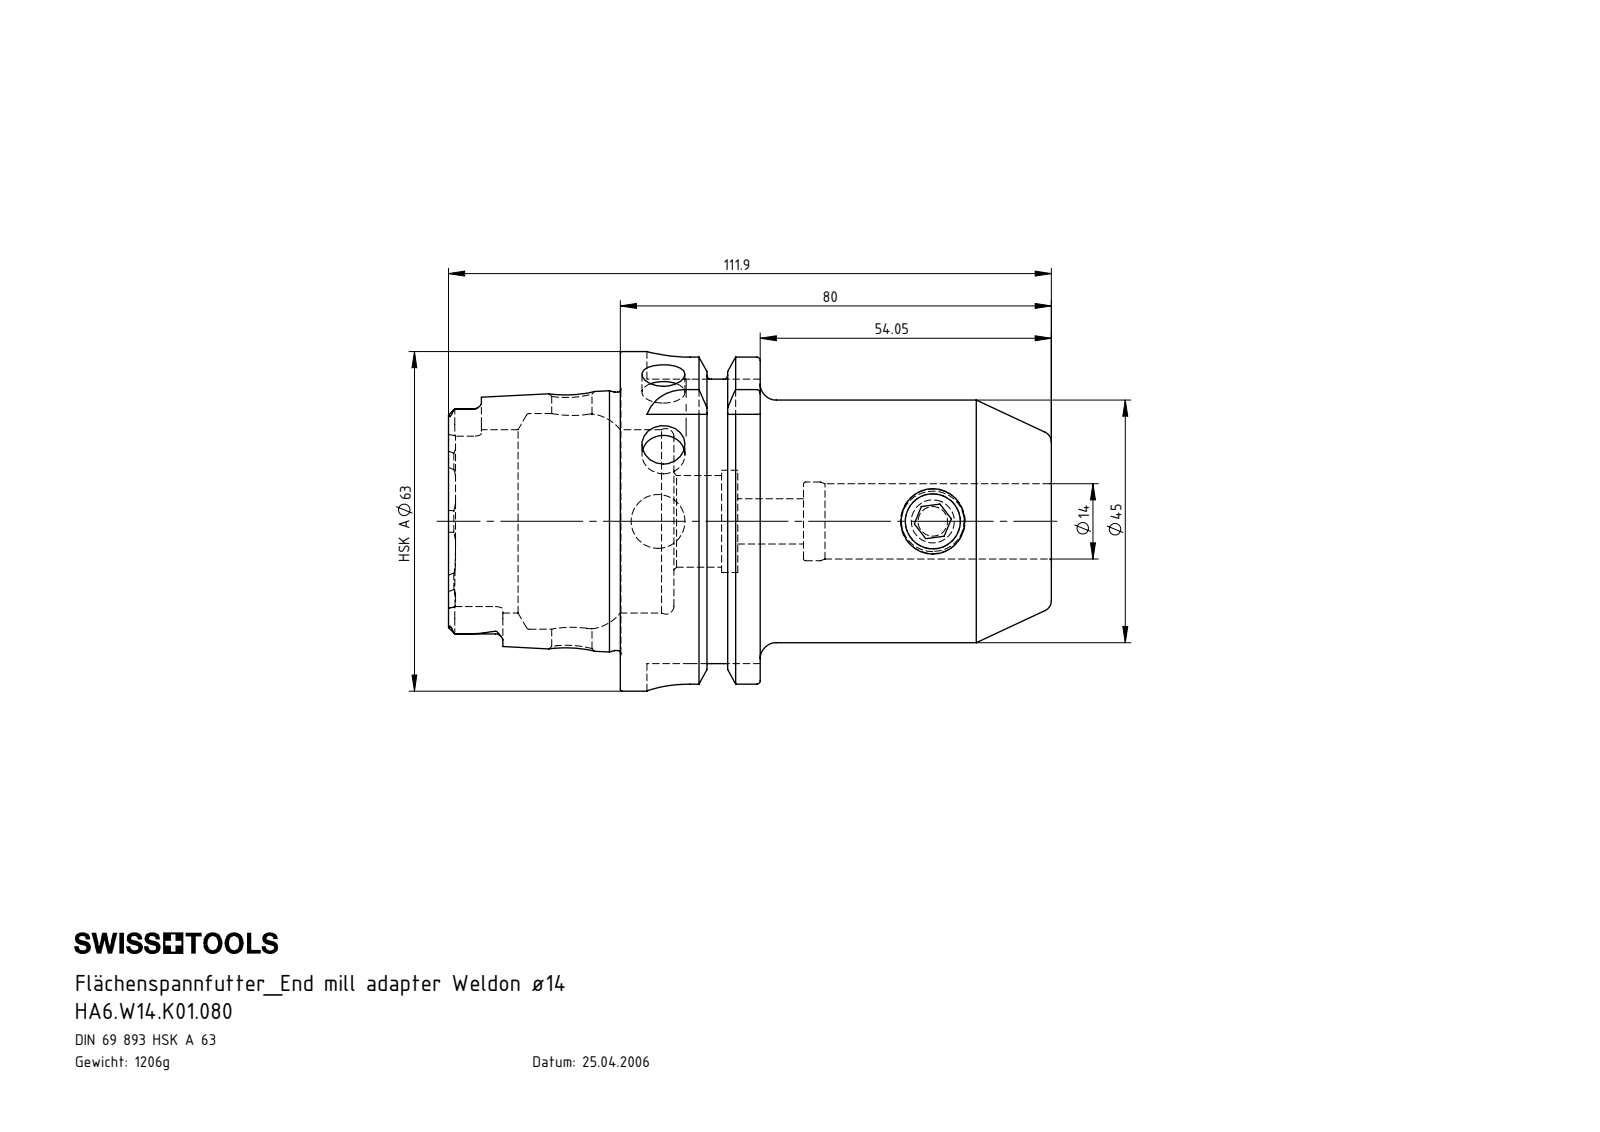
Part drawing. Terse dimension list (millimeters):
name: HA6-W14.K01.080; W12-ER1.001.016; HA6-W14.K01.080_B_Fertigbearbeitung
written by: SolidWorks 2012 (AUTOMOTIVE_DESIGN)
unit: mm
bodies: 2 solids, 208 faces (58 planar, 57 cylindrical, 93 other)
size: 111.9 × 63 × 63
volume: 153 616 mm³; area: 32 530 mm²
holes: 2× ⌀8, 1× ⌀7.5, 1× ⌀8.4, 1× ⌀10, 1× ⌀10.25, 1× ⌀14, 1× ⌀14.6, 1× ⌀17, 1× ⌀19, 1× ⌀34, 1× ⌀40
bosses: 1× ⌀63, 1× ⌀54.95, 1× ⌀47.94, 1× ⌀45, 1× ⌀12
rounds: 6× R1.4, 4× R2.88, 4× R8
face distances: 25.95, 16, 9.95, 80, 70.05, 54.05, 31.9, 41.85, 57.85, 111.9
hole spacings: 51
